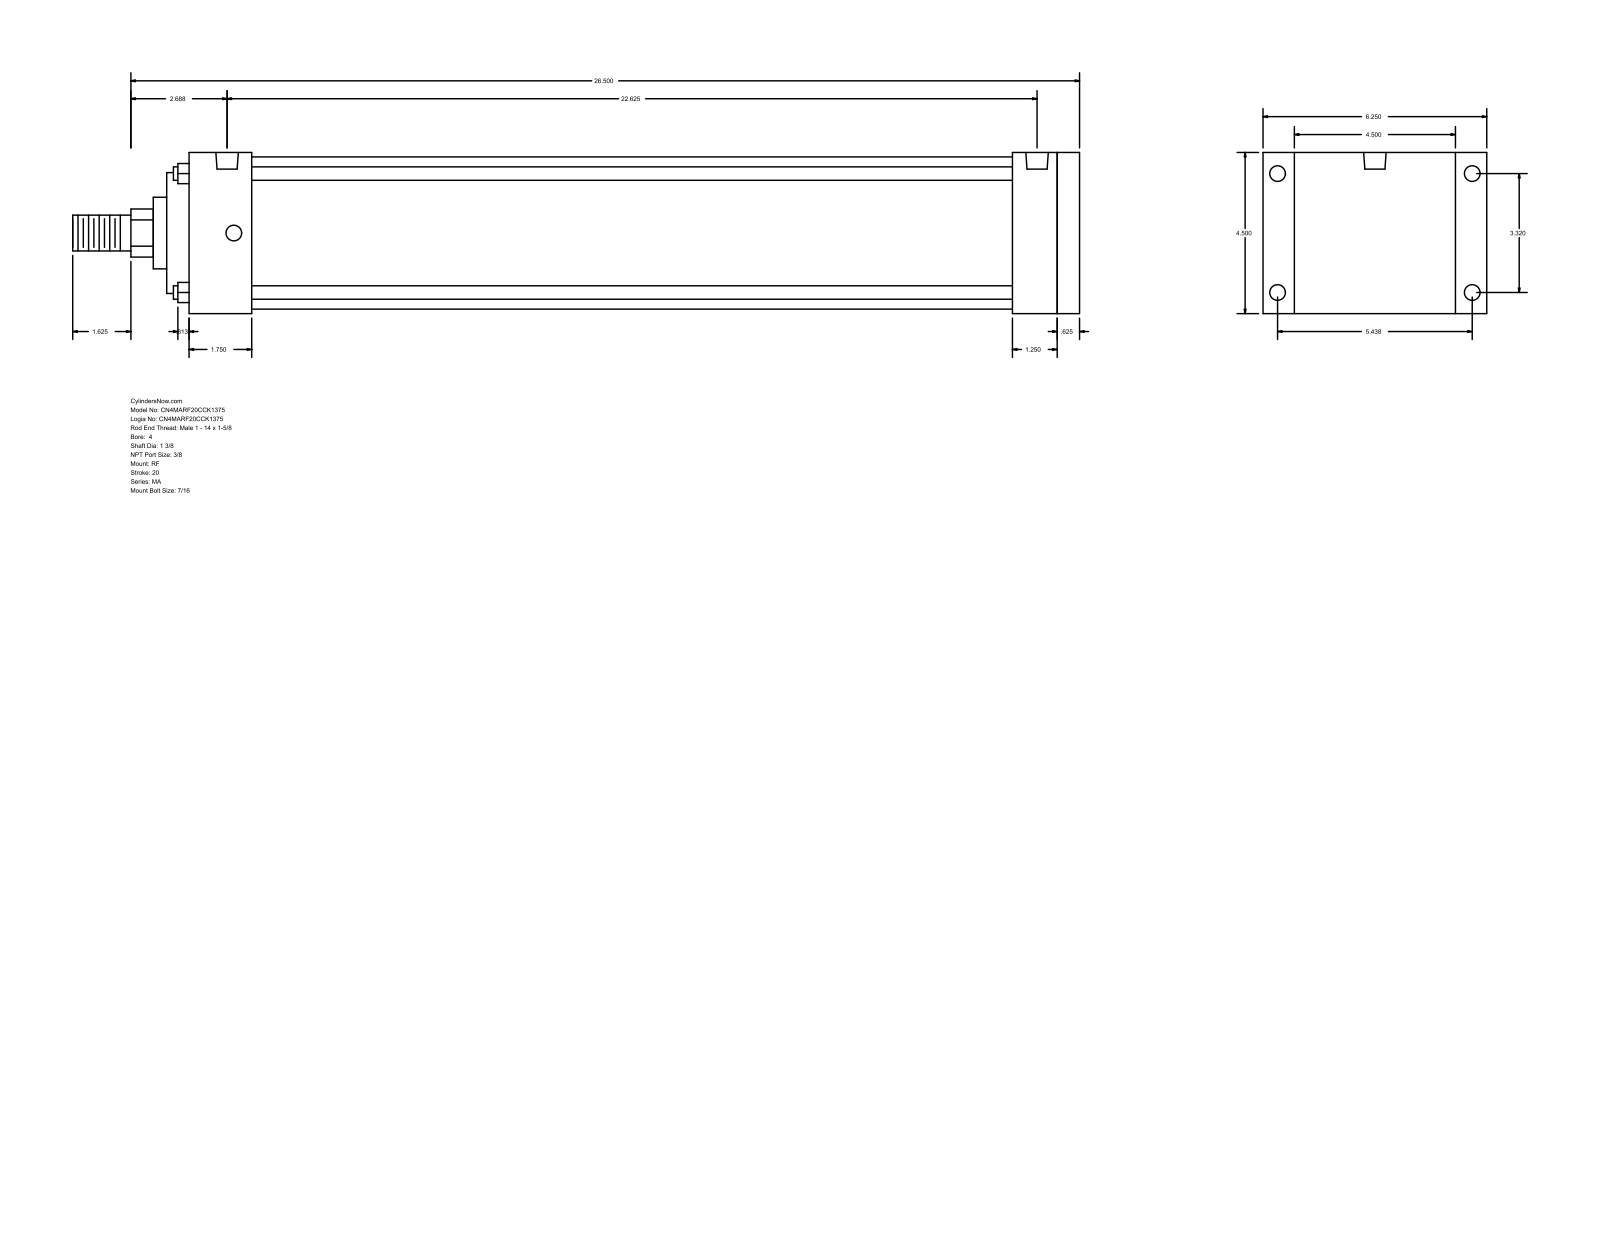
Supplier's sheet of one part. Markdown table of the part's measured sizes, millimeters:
| quantity | value |
| --- | --- |
| part name | MA_RF__0400_1.375 |
| STEP written by | GSSL Pune (CONFIG_CONTROL_DESIGN) |
| units | millimeters |
| bodies | 0 solids, 94 faces (65 planar, 29 cylindrical, 0 other) |
| overall size | 714.38 × 158.75 × 114.3 |
| round holes (diameter × count) | 11.11 × 8, 15.93 × 2 |
| round bosses / shafts (diameter × count) | 9.53 × 4, 107.95 × 1, 85.72 × 1, 50.8 × 1, 34.92 × 1, 25.4 × 1 |
| partial cylindrical surfaces (radius × count) | 17.06 × 1 |
| main face-to-face distances | 114.3, 631.83, 15.87, 615.96, 647.7, 22.23, 136.53, 600.08, 584.21, 31.75 |
| hole center spacings | 4.77, 84.32, 138.12, 161.82, 565.14, 569.91, 574.68 |
